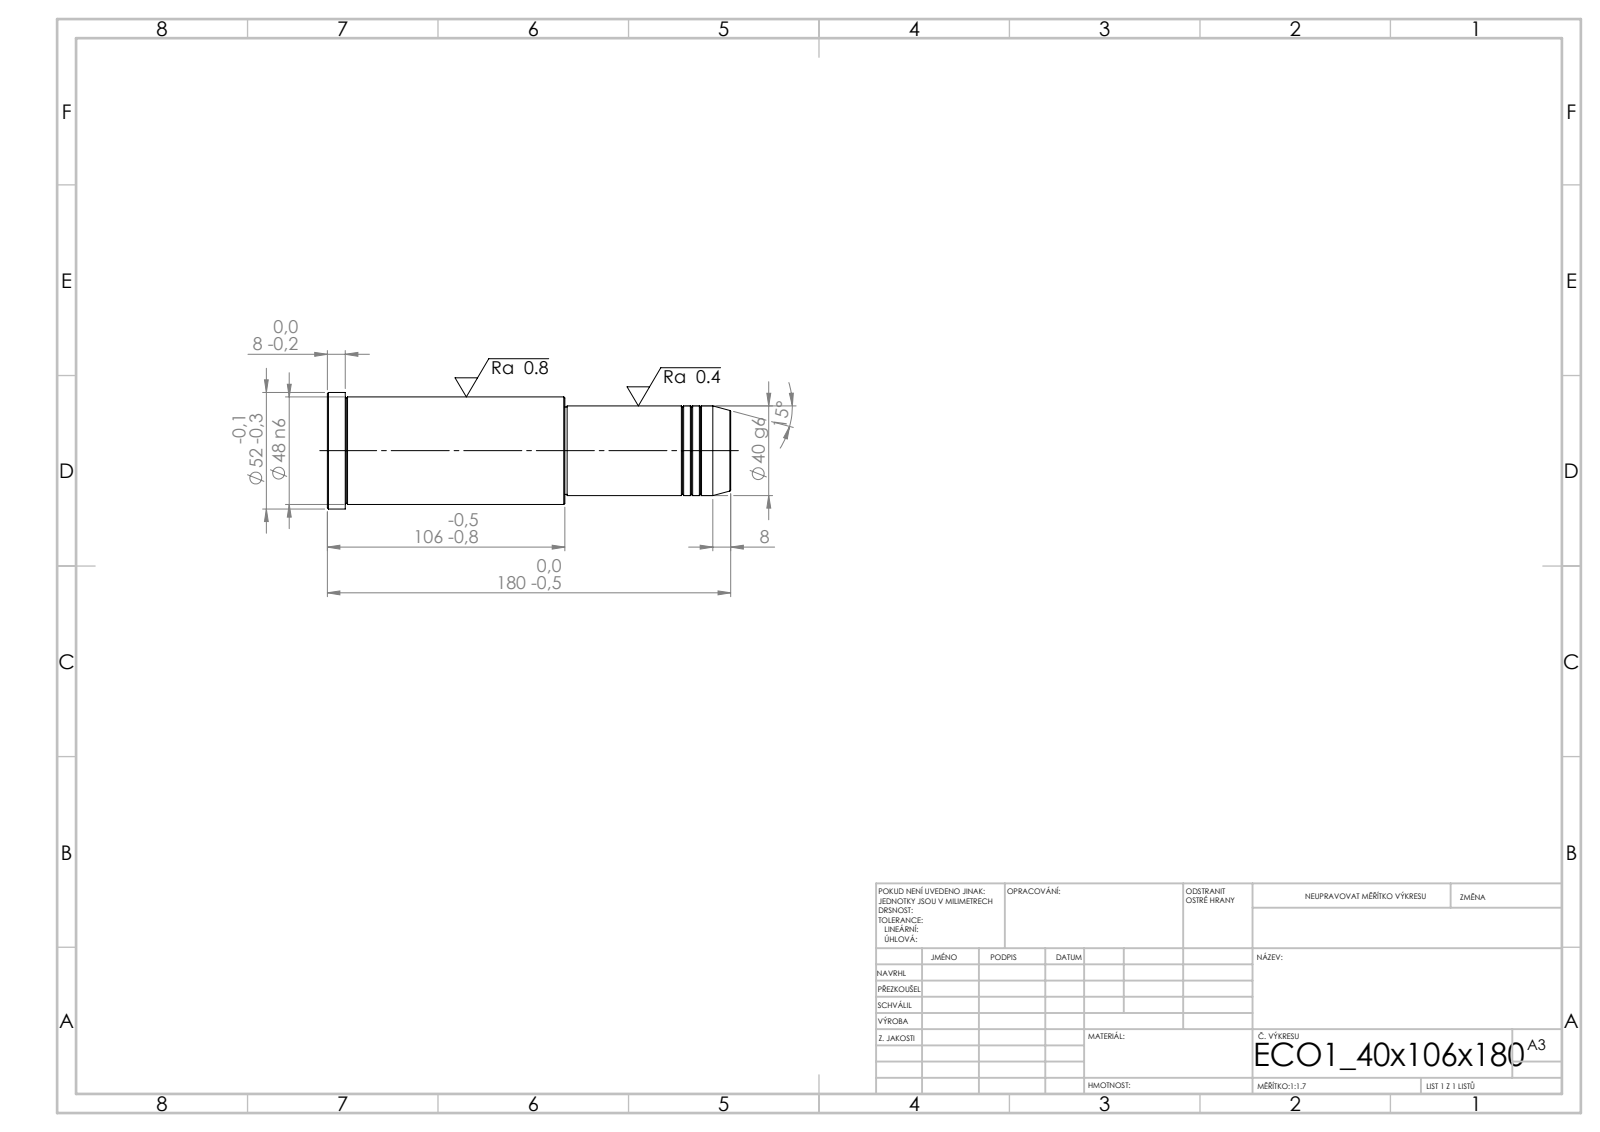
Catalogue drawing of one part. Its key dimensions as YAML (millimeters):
step_written_by: "SolidWorks 2019 (CONFIG_CONTROL_DESIGN)"
units: millimeters
bodies: {solids: 1, faces: 43, planar: 5, cylindrical: 14, other: 24}
overall_size: [180, 52, 52]
volume: 285969
surface_area: 29660
round_bosses_or_shafts:
  - {diameter: 52, count: 1}
  - {diameter: 48, count: 1}
  - {diameter: 40, count: 1}
  - {diameter: 39, count: 1}
face_to_face_distances: [180, 74, 106, 172, 98, 8, 73, 1, 99, 107]
